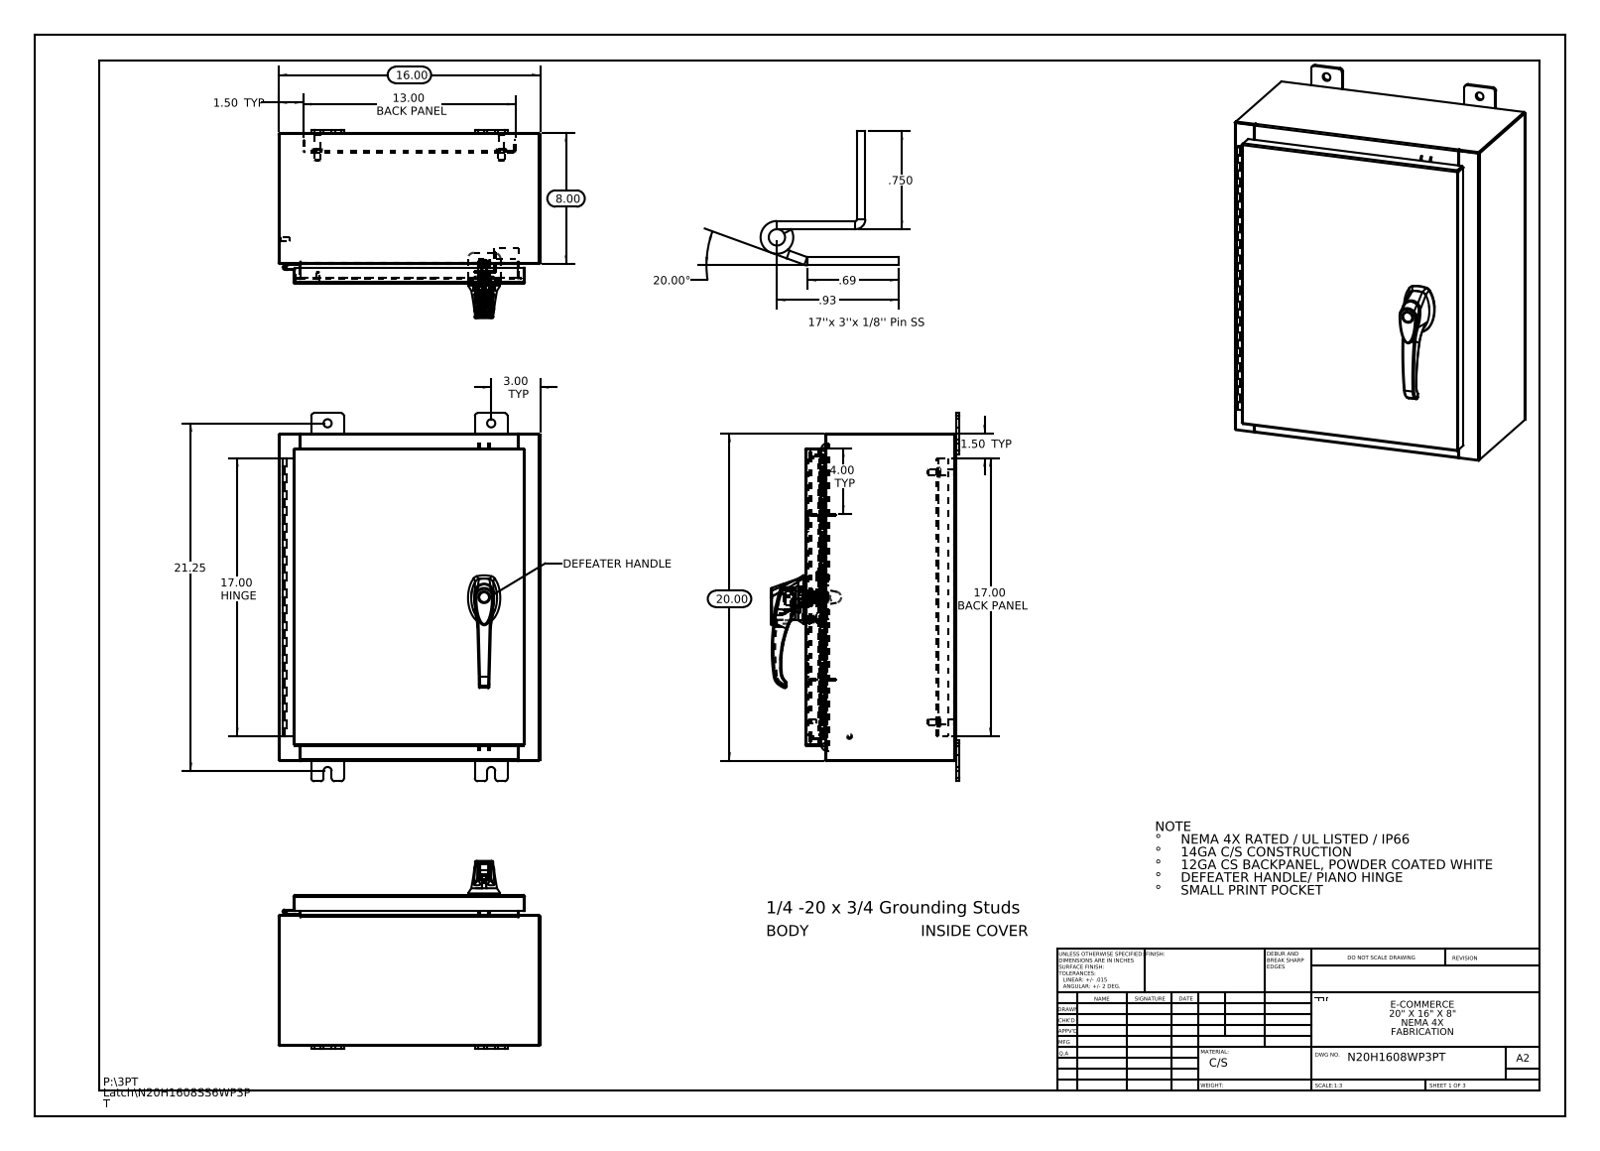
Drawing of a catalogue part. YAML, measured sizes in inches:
part_name: "N20H1608SS6WP3PT Body; 00005090; N20H1608SS6WP3PT Bottom; N20H1608SS6WP3PT Mounting Feet (+8 more)"
step_written_by: "SolidWorks 2013 (CONFIG_CONTROL_DESIGN)"
units: inches
bodies: {solids: 31, faces: 2316, planar: 817, cylindrical: 845, other: 654}
overall_size: [22.5, 16, 11.495]
volume: 142.4
surface_area: 3517
round_holes:
  - {diameter: 0.5, count: 8}
  - {diameter: 0.25, count: 4}
  - {diameter: 0.138, count: 3}
  - {diameter: 0.161, count: 3}
  - {diameter: 0.079, count: 2}
  - {diameter: 0.203, count: 2}
  - {diameter: 0.313, count: 2}
  - {diameter: 0.437, count: 2}
  - {diameter: 0.125, count: 1}
  - {diameter: 0.125, count: 1}
  - {diameter: 0.197, count: 1}
  - {diameter: 0.276, count: 1}
round_bosses_or_shafts:
  - {diameter: 0.625, count: 4}
  - {diameter: 0.375, count: 4}
  - {diameter: 0.33, count: 4}
  - {diameter: 1.181, count: 1}
  - {diameter: 0.748, count: 1}
  - {diameter: 0.68, count: 1}
  - {diameter: 0.661, count: 1}
  - {diameter: 0.639, count: 1}
partial_cylinders:
  - {radius: 0.118, count: 37}
  - {radius: 0.006, count: 33}
  - {radius: 0.19, count: 24}
  - {radius: 0.013, count: 22}
  - {radius: 0.088, count: 18}
  - {radius: 0.039, count: 15}
  - {radius: 0.028, count: 12}
  - {radius: 0.008, count: 6}
face_to_face_distances: [0.075, 9.126, 15.925, 9.051, 9.201, 19.925, 0.104, 1, 1.075, 8.051]
hole_center_spacings: [3.404, 11.975, 0.295, 0.625, 0.841, 1.25, 1.313, 1.561]
